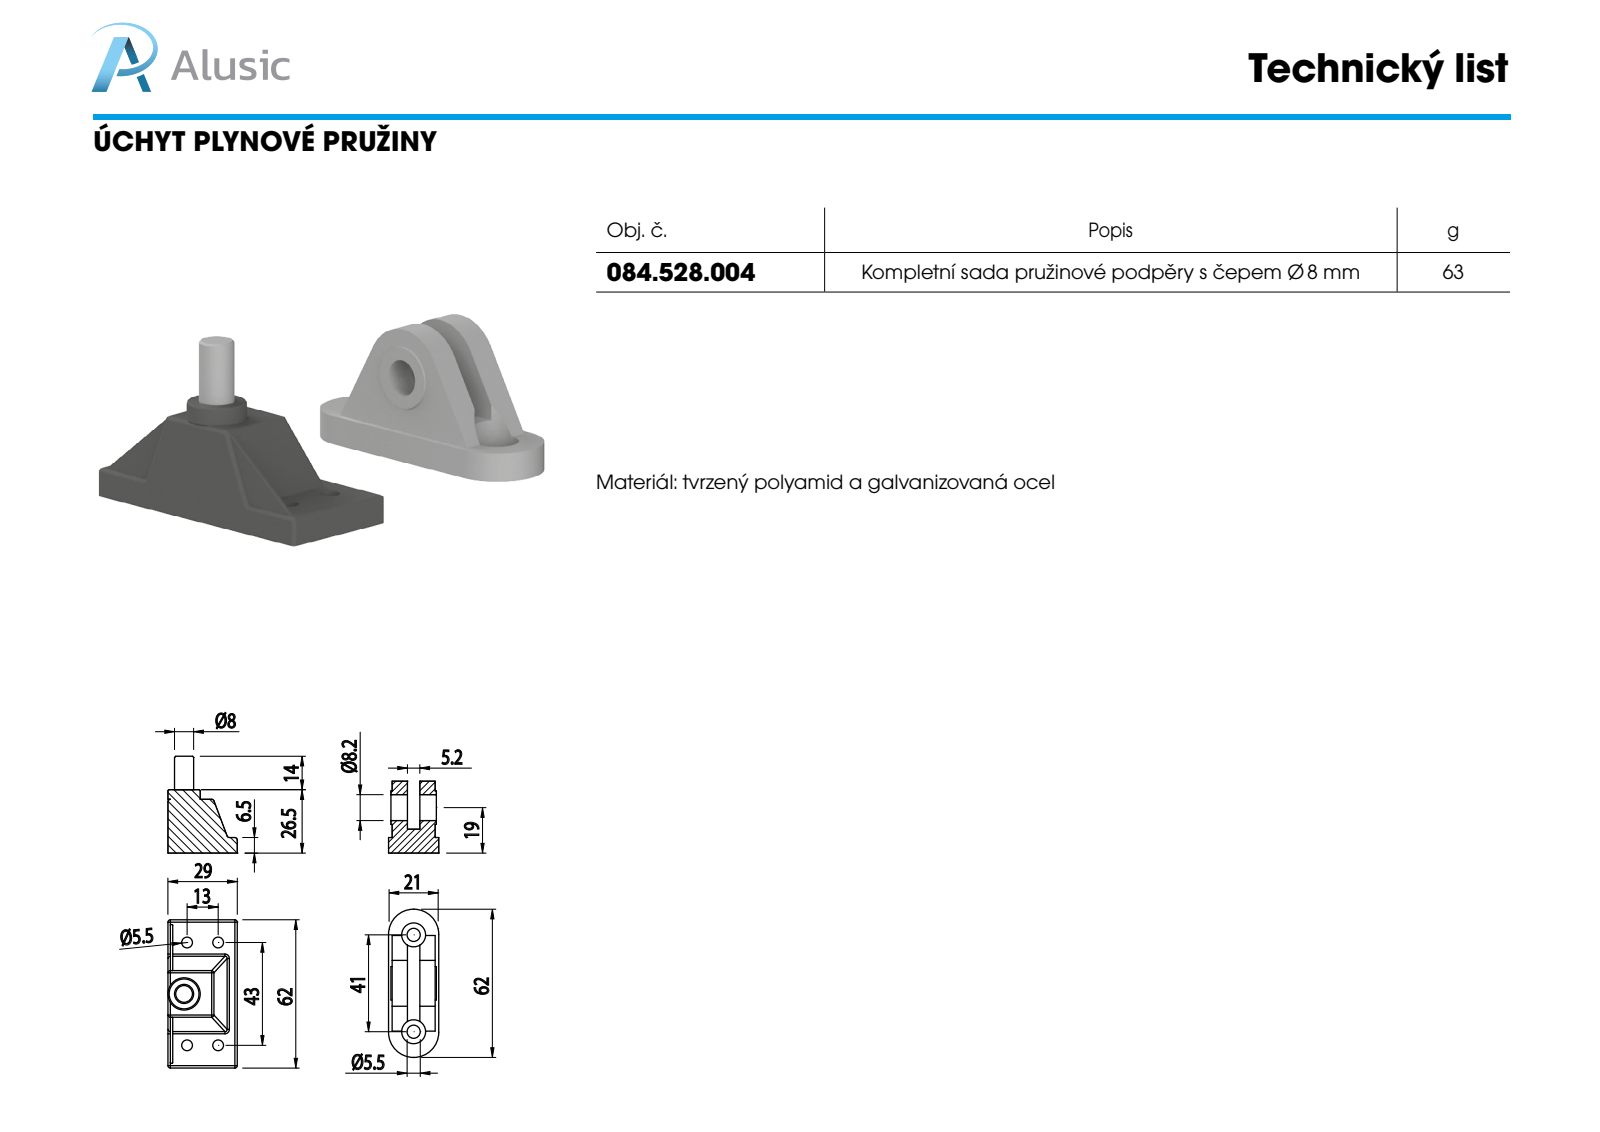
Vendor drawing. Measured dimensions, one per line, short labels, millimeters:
name: 084.528.004; P101; P100
written by: SolidWorks 2011 (CONFIG_CONTROL_DESIGN)
unit: mm
bodies: 3 solids, 112 faces (37 planar, 57 cylindrical, 18 other)
size: 93.37 × 82.28 × 42.58
volume: 36 434 mm³; area: 13 419 mm²
holes: 6× ⌀5.5, 2× ⌀10, 1× ⌀8.2
bosses: 1× ⌀14, 1× ⌀13.5, 1× ⌀8
rounds: 19× R1, 4× R0.2, 2× R10.5, 1× R11.07
face distances: 12.51, 6.5, 6.4, 11.6, 6.01, 1, 1.5, 7.9, 13.1, 19.5
hole spacings: 13, 43, 44.92, 28.6, 39.19, 40.5, 64.57, 65.76
